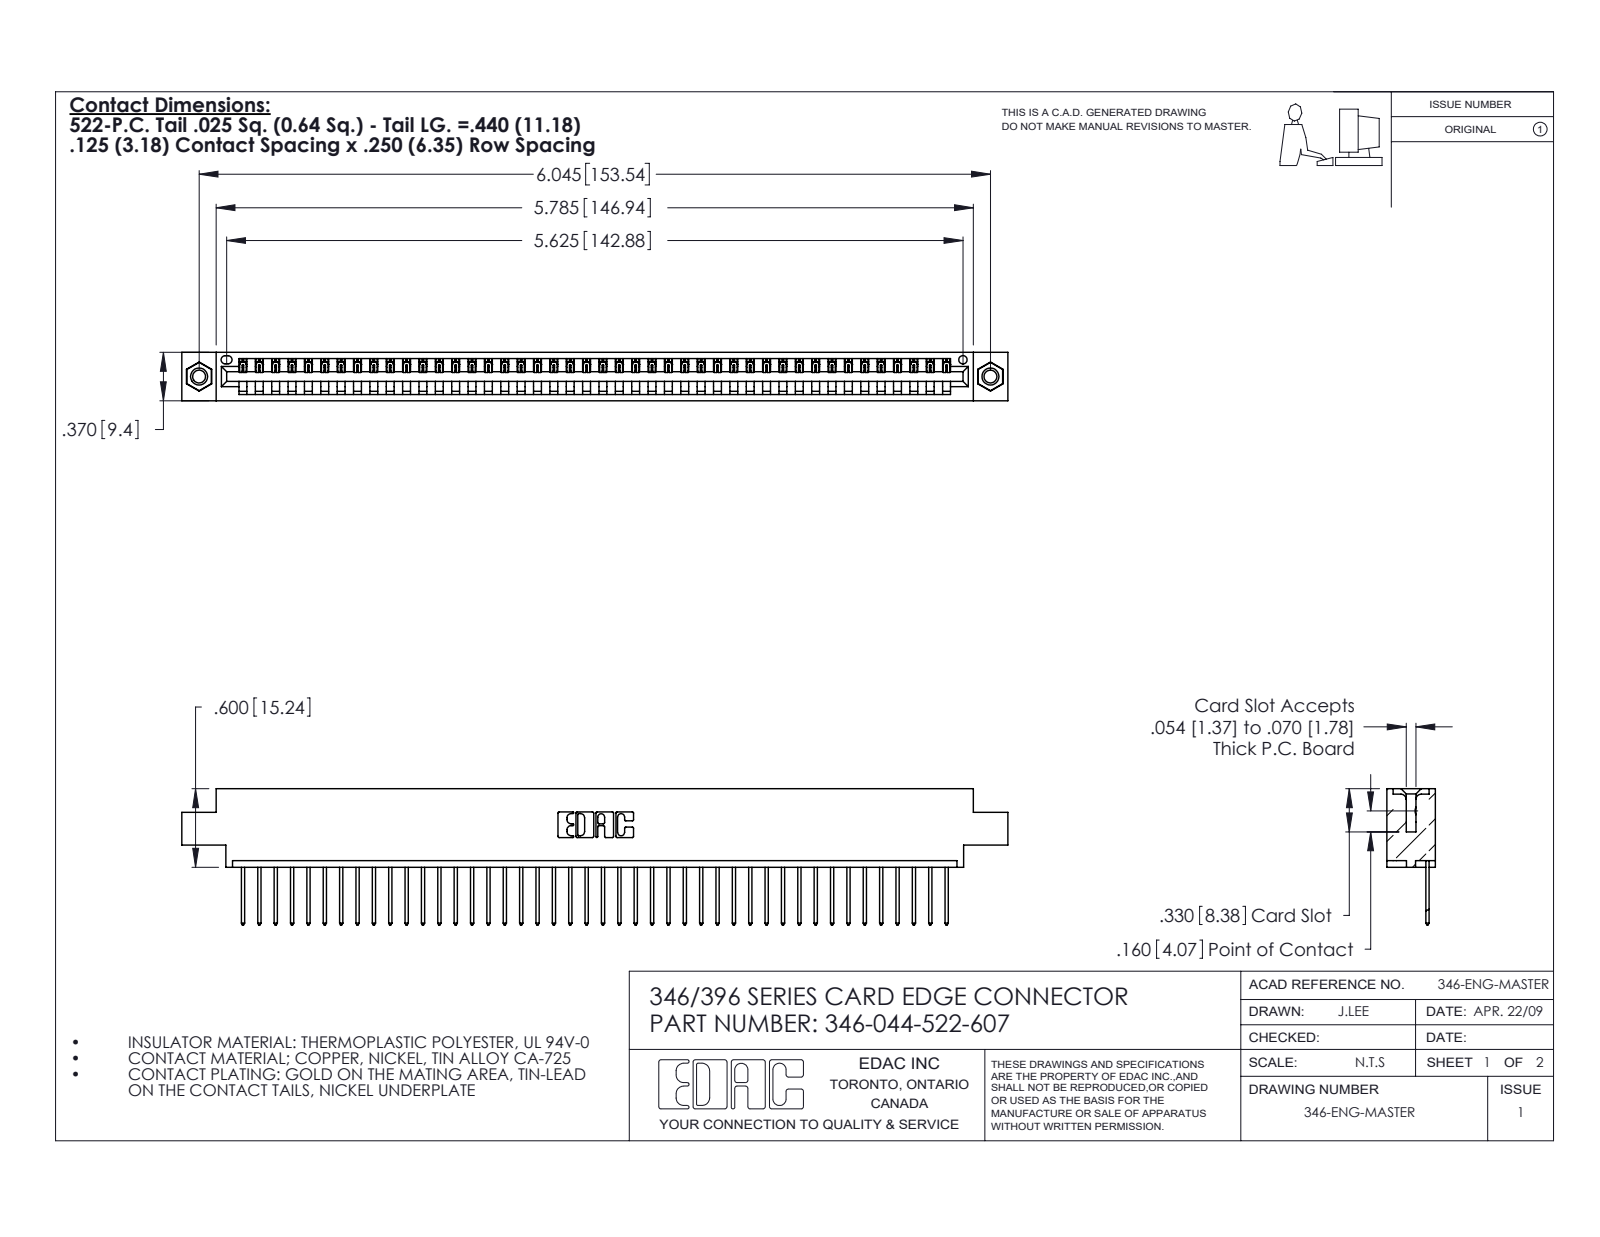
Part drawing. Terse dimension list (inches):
name: 345-250-001_345-250-005-103; 346 Part_0.170 Offset - 0.156 Dia-TI; 346-044-522-607; 345-292-001_345-293-122
written by: SolidWorks 2020 (CONFIG_CONTROL_DESIGN)
unit: in
bodies: 47 solids, 2738 faces (1872 planar, 850 cylindrical, 16 other)
size: 6.31 × 1.04 × 0.37
volume: 0.927 in³; area: 30.02 in²
holes: 2× ⌀0.098, 2× ⌀0.125, 2× ⌀0.156, 1× ⌀0.064
bosses: 2× ⌀0.155
rounds: 88× R0.006, 88× R0.01, 22× R0.01, 6× R0.007, 6× R0.031, 3× R0.026, 2× R0.031, 2× R0.04
face distances: 0.048, 0.322, 0.37, 0.25, 0.072, 0.298, 0.025, 0.222, 0.148, 0.1
hole spacings: 0.246, 5.836, 6.045
